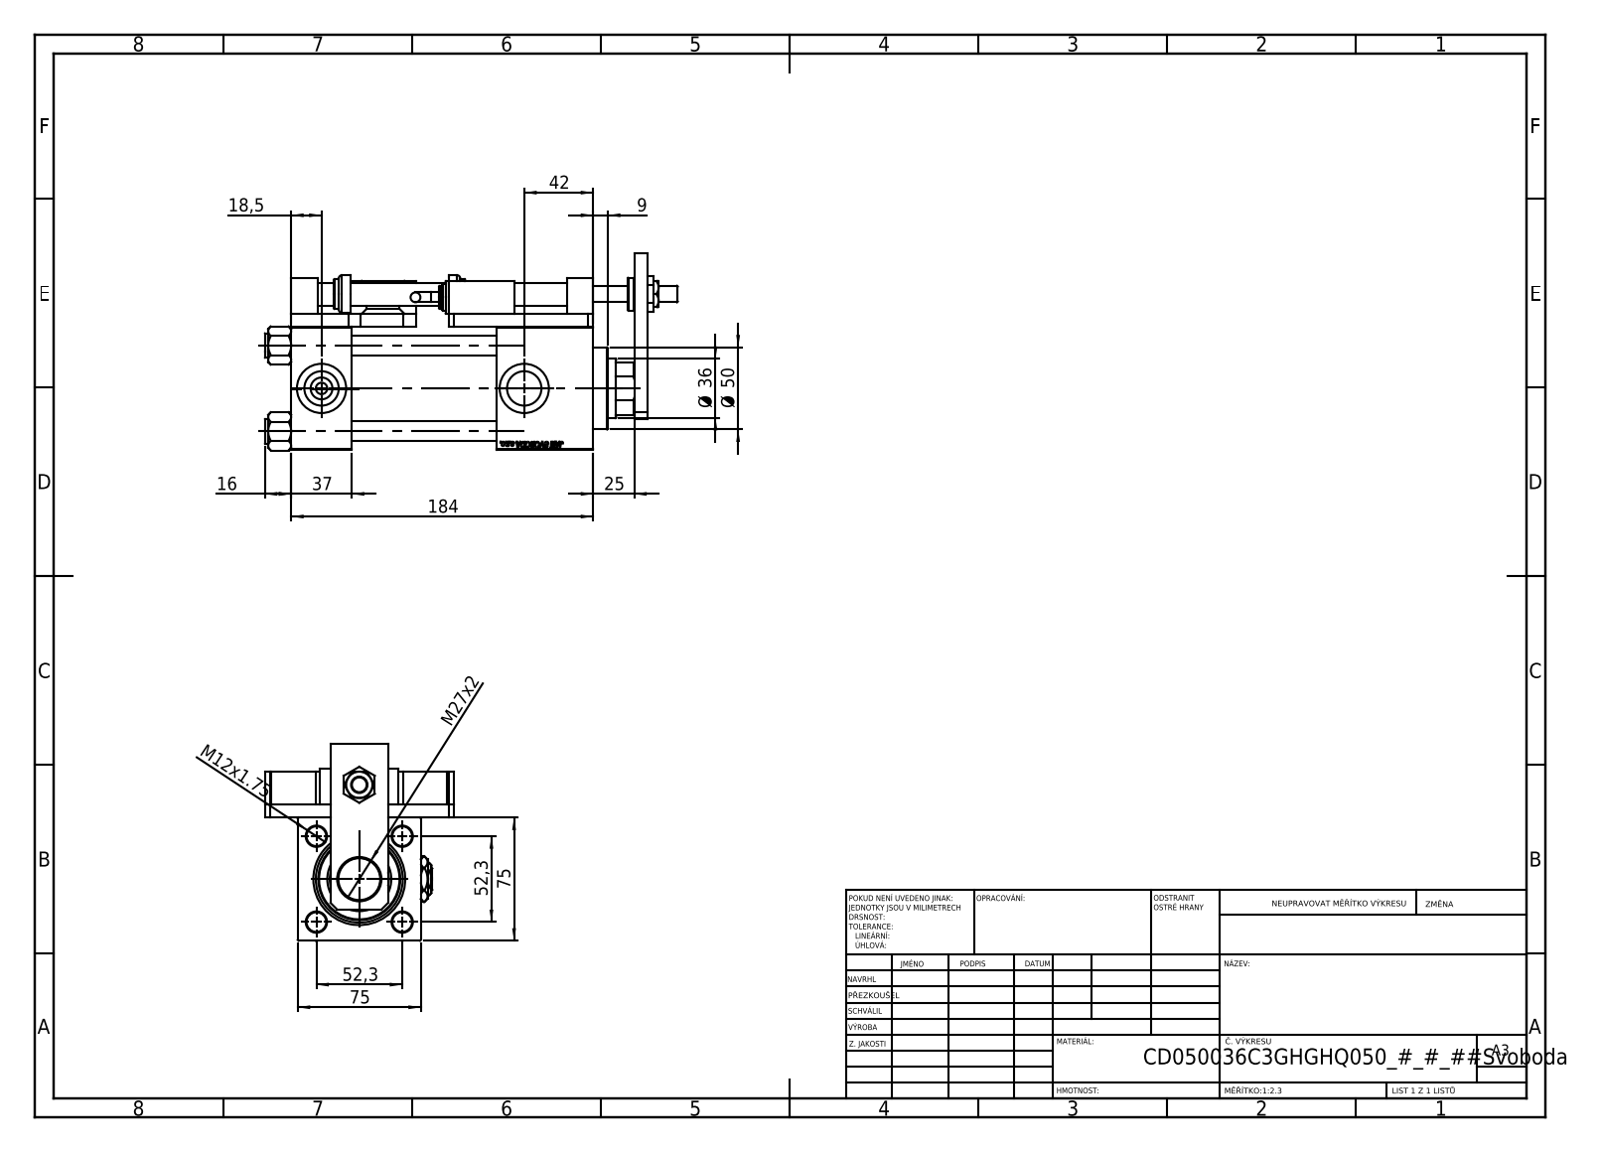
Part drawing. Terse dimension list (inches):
name: V215CD_SWITCH_Q_SWITCH; V215CD_Body_C; V215CD_SWITCH_Q_TYC; Zatka_pro_OIL_PORT (+7 more)
written by: SolidWorks 2019 (CONFIG_CONTROL_DESIGN)
unit: in
bodies: 26 solids, 1477 faces (694 planar, 166 cylindrical, 617 other)
size: 9.902 × 4.735 × 4.528
volume: 61.01 in³; area: 405.7 in²
holes: 4× ⌀0.335, 4× ⌀0.472, 4× ⌀0.531, 2× ⌀0.276, 2× ⌀0.825, 2× ⌀1.181, 1× ⌀0.394, 1× ⌀0.551, 1× ⌀1.004, 1× ⌀1.063, 1× ⌀1.417, 1× ⌀1.535
bosses: 4× ⌀0.591, 3× ⌀0.787, 2× ⌀0.63, 2× ⌀0.551, 2× ⌀0.236, 1× ⌀2.205, 1× ⌀1.969, 1× ⌀0.906
rounds: 4× R0.295, 1× R0.689
face distances: 0.315, 2.953, 0.787, 3.268, 1.457, 7.244, 2.323, 5.787, 0.984, 3.622
hole spacings: 1.456, 2.059, 1.26, 1.607, 2.912, 3.45, 6.614, 6.733
